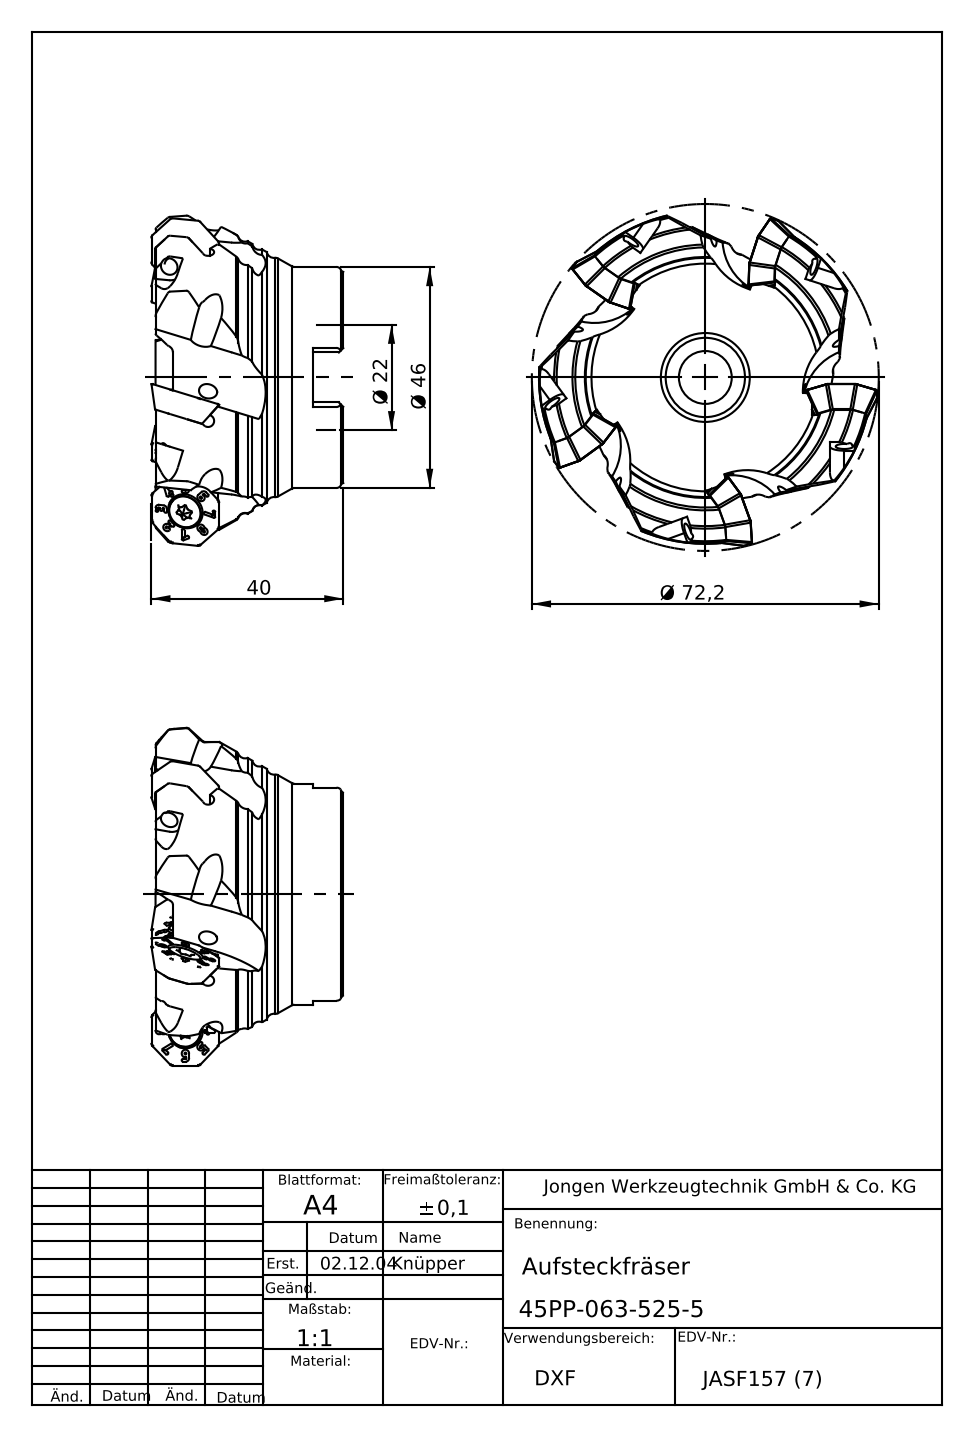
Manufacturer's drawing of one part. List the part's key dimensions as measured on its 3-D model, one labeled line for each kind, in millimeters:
Part name (STEP PRODUCT): 45PP-063-525-5
STEP written by: SolidWorks 2016 (AUTOMOTIVE_DESIGN)
Units: millimetres
Bodies: 1 solid, 168 faces (38 planar, 42 cylindrical, 88 other)
Overall size (bounding box): 72.02 × 72.02 × 39.99
Volume: 83 283 mm³ · Surface area: 17 147 mm²
Round holes (diameter × count): ⌀3 ×5, ⌀11 ×1, ⌀16.5 ×1, ⌀22 ×1, ⌀22.15 ×1, ⌀22.3 ×1
Round bosses / shafts (diameter × count): ⌀46 ×1
Partial cylindrical surfaces — rounded edges, fillets, slot ends (radius × count): R2.5 ×5, R12.5 ×5, R31.68 ×1
Main face-to-face distances: 35.5, 6.3, 29.2, 20, 13.7, 15.5, 24.5, 18.2, 4.5, 11
